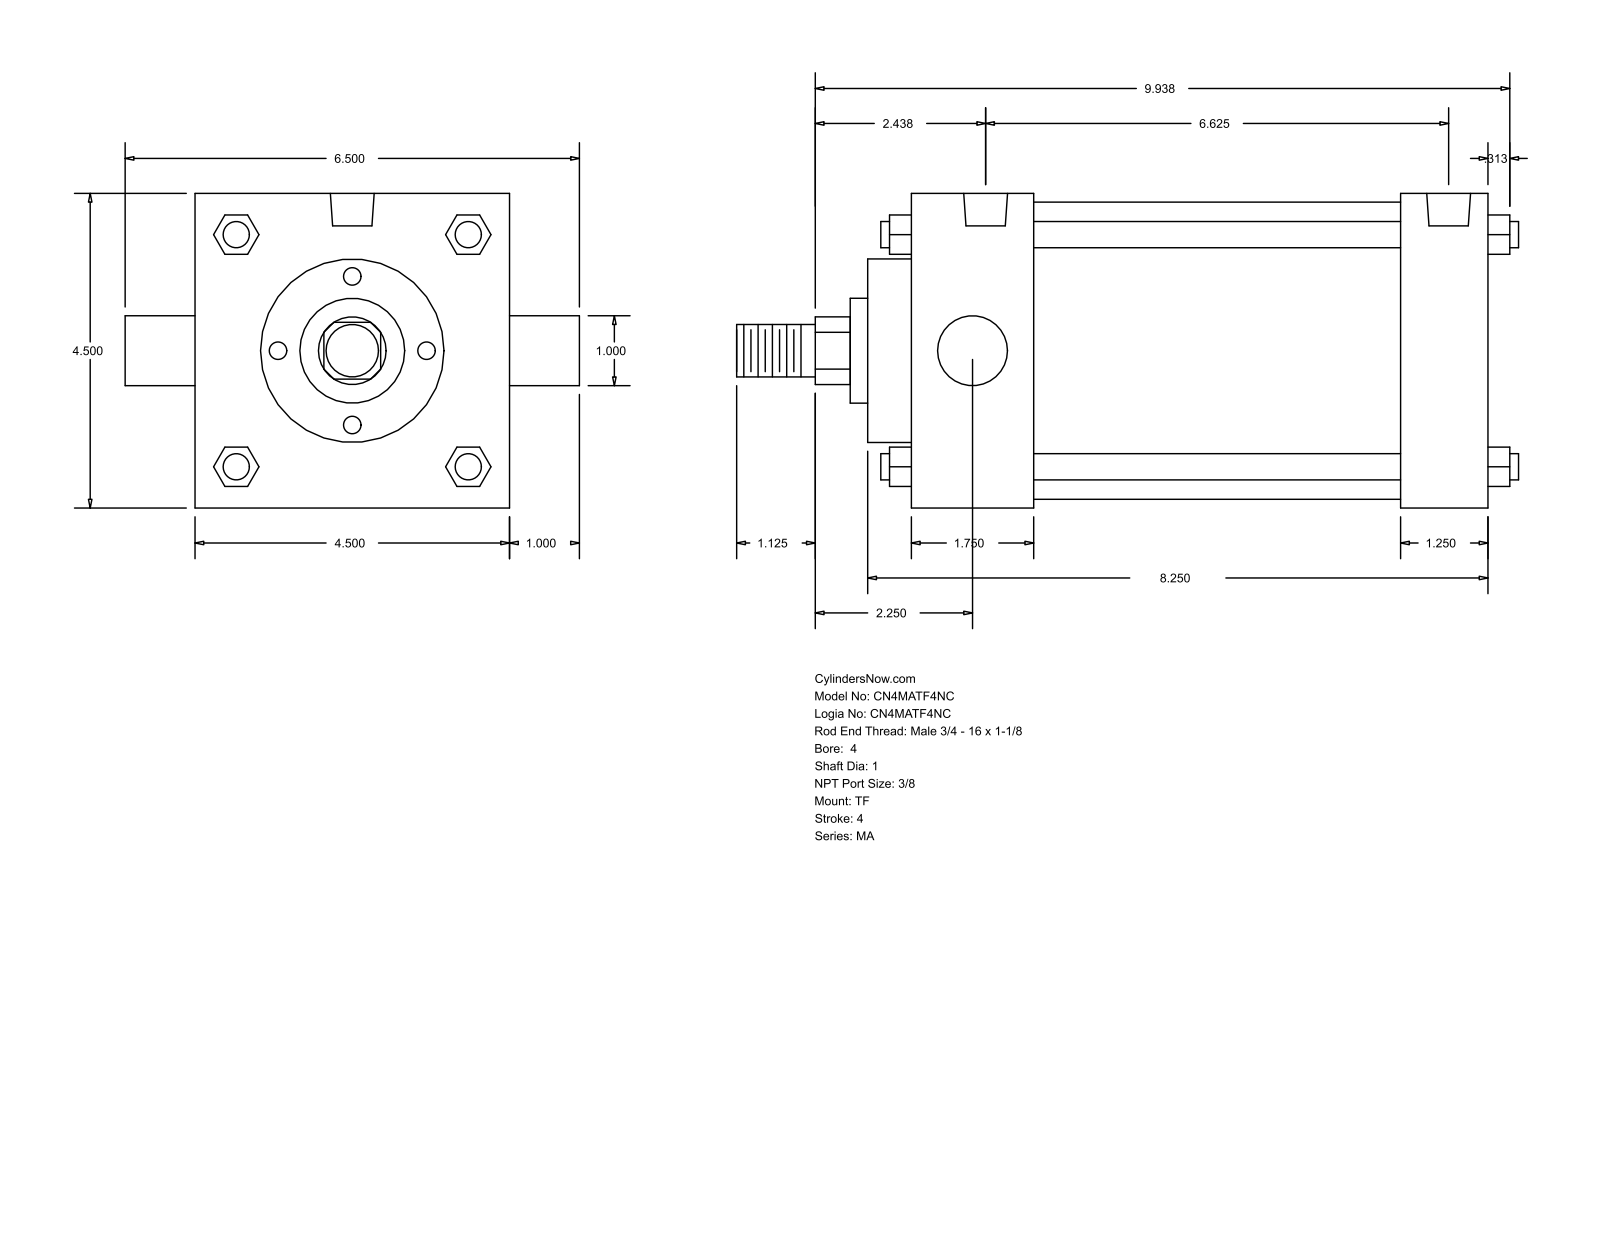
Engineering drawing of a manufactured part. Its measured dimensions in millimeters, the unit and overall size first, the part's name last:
Units: millimetres
Overall size (bounding box): 284.16 × 165.1 × 114.3
Round holes (diameter × count): ⌀11.11 ×3, ⌀15.93 ×2
Round bosses / shafts (diameter × count): ⌀9.53 ×4, ⌀25.4 ×2, ⌀107.95 ×1, ⌀66.67 ×1, ⌀38.1 ×1, ⌀19.05 ×1
Partial cylindrical surfaces — rounded edges, fillets, slot ends (radius × count): R12.29 ×1
Main face-to-face distances: 114.3, 209.55, 177.8, 31.75, 44.46, 133.34, 165.09, 225.42, 15.87, 60.33
Hole centre spacings: 4.76, 163.52, 158.76, 168.28
Bodies: 0 solids, 122 faces (93 planar, 29 cylindrical, 0 other)
Part name (STEP PRODUCT): MA_TF__0400_1
STEP written by: GSSL Pune (CONFIG_CONTROL_DESIGN)
